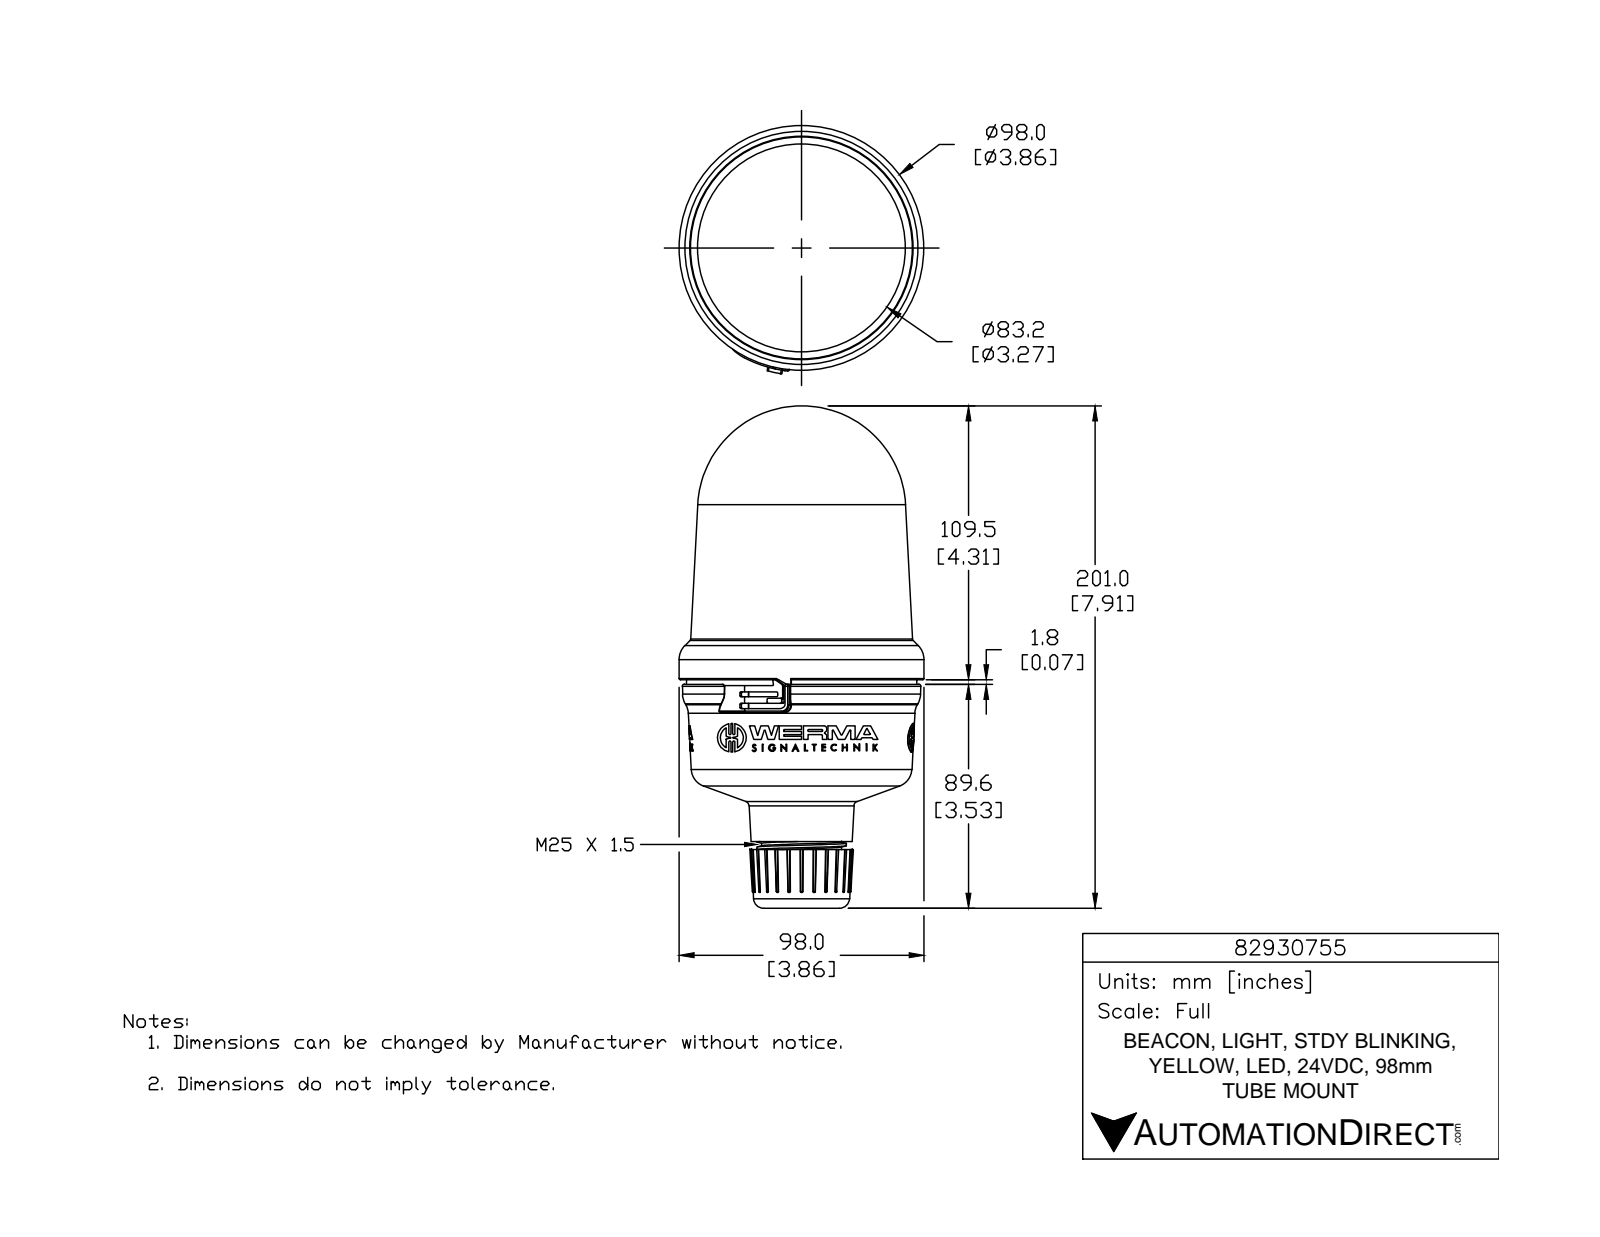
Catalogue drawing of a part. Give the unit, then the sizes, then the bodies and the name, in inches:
Units: inches
Overall size (bounding box): 7.914 × 3.912 × 3.858
Round holes (diameter × count): ⌀0.078 ×3, ⌀1.013 ×1, ⌀1.024 ×1
Round bosses / shafts (diameter × count): ⌀0.452 ×3, ⌀0.113 ×3, ⌀3.858 ×1, ⌀1.409 ×1, ⌀1.261 ×1
Partial cylindrical surfaces — rounded edges, fillets, slot ends (radius × count): R0.02 ×12, R0.007 ×9, R0.007 ×6, R0.016 ×6, R0.016 ×6, R0.016 ×6, R0.262 ×6, R0.006 ×3
Main face-to-face distances: 2.214, 0.462, 2.676, 0.335, 0.127, 2.548, 2.603, 2.476, 2.141, 0.073
Volume: 54.7 in³ · Surface area: 91.39 in²
Bodies: 1 solid, 1006 faces (554 planar, 189 cylindrical, 263 other)
Part name (STEP PRODUCT): 82930755
STEP written by: SolidWorks 2015 (AUTOMOTIVE_DESIGN)
